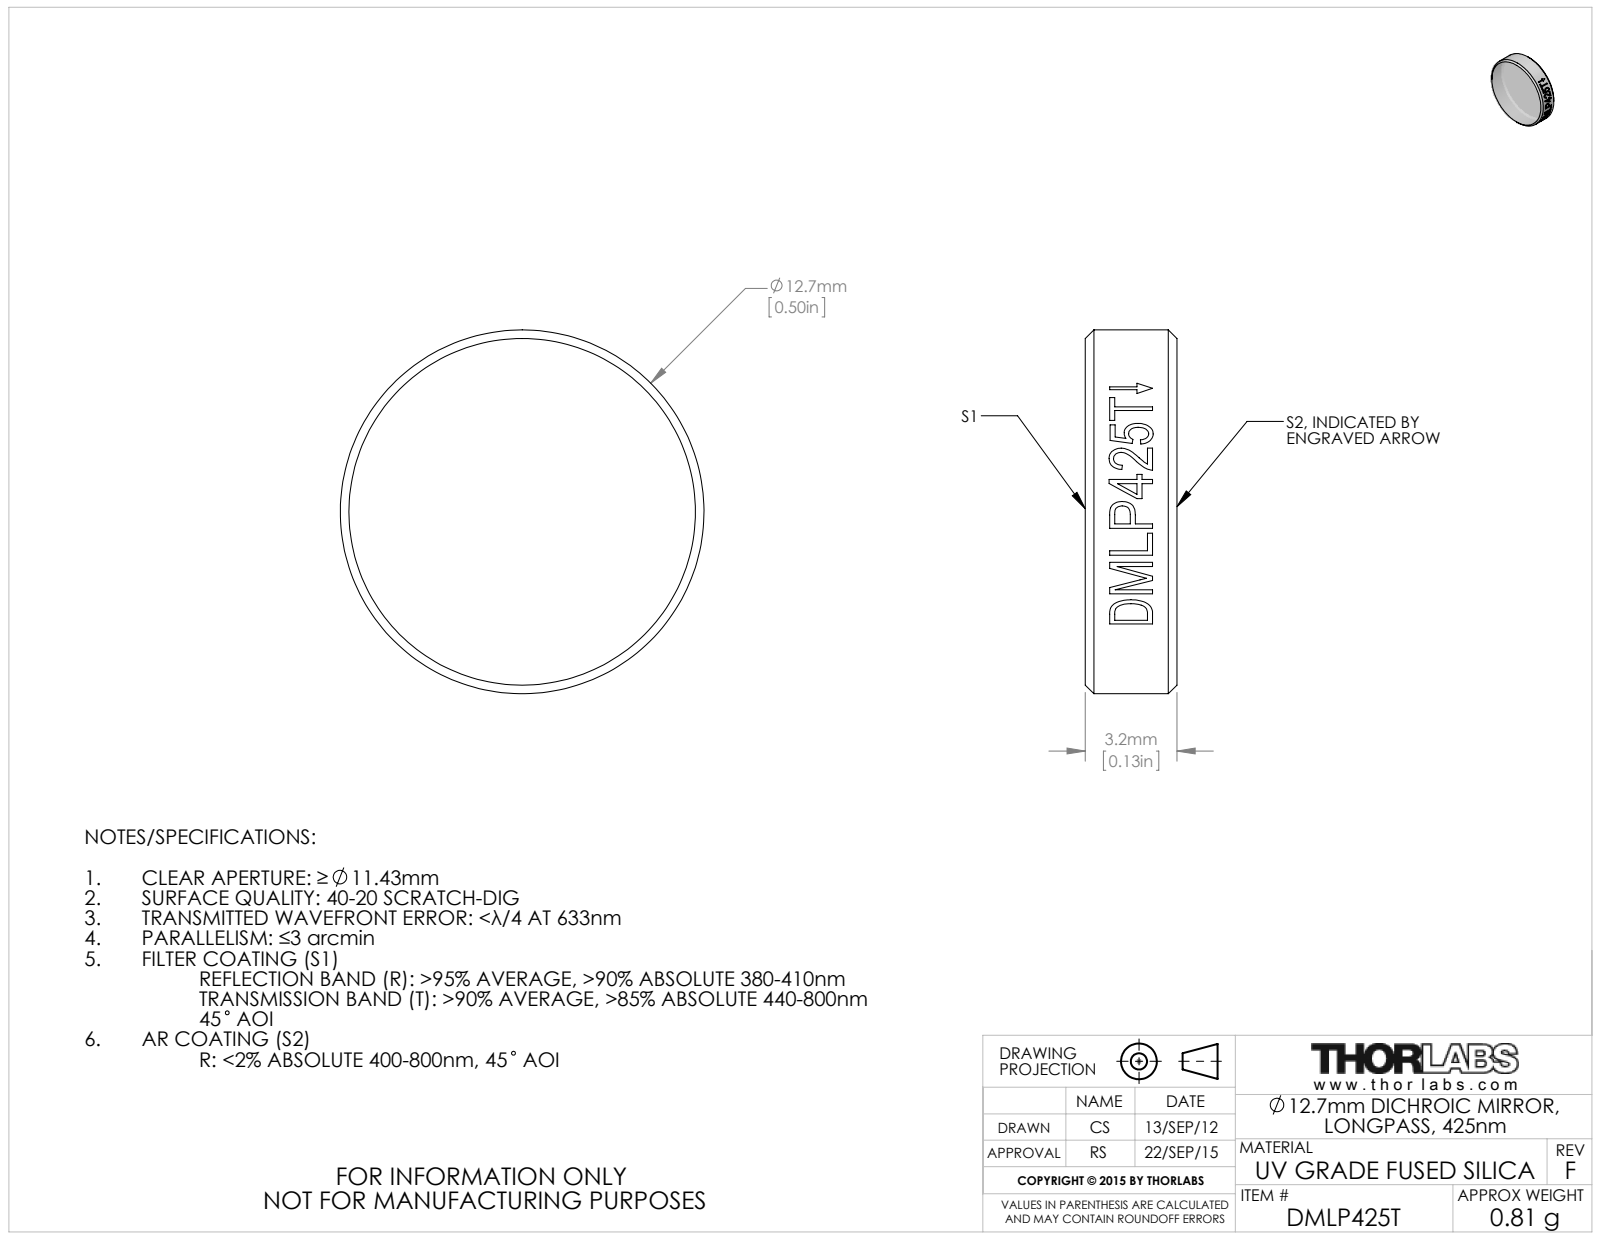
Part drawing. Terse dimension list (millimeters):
name: 24961-E0W
written by: SolidWorks 2011 (CONFIG_CONTROL_DESIGN)
unit: mm
bodies: 0 solids, 20 faces (2 planar, 14 cylindrical, 4 other)
size: 12.7 × 12.7 × 3.2
bosses: 1× ⌀12.7
face distances: 3.2
